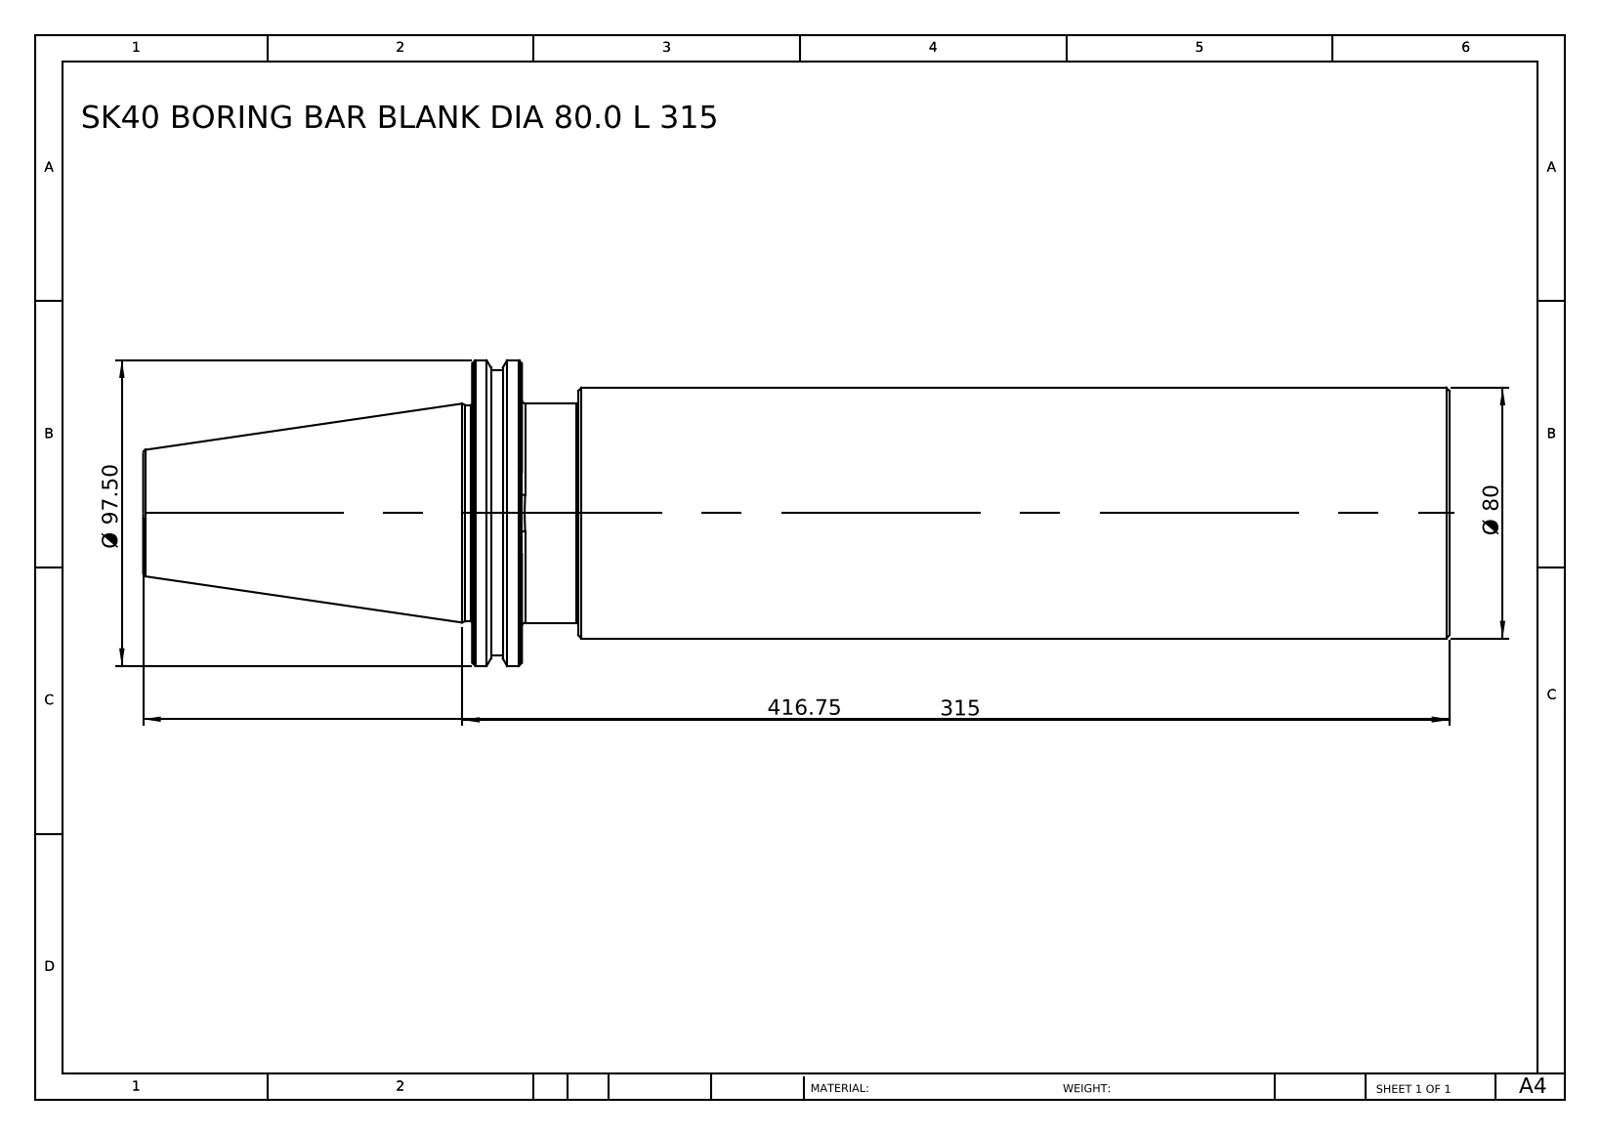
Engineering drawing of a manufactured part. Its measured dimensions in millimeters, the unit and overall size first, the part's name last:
Units: millimetres
Overall size (bounding box): 416.75 × 97.5 × 97.5
Round bosses / shafts (diameter × count): ⌀97.5 ×1, ⌀91 ×1, ⌀80 ×1, ⌀70 ×1, ⌀69 ×1
Main face-to-face distances: 311.8, 295.9, 15.9, 416.75, 120.85, 104.95, 277.9, 18, 33.9, 138.85
Volume: 1 839 000 mm³ · Surface area: 112 311 mm²
Bodies: 1 solid, 72 faces (7 planar, 12 cylindrical, 53 other)
Part name (STEP PRODUCT): SK50 BORING BAR BLANK DIA 80.0 L 315
STEP written by: SolidWorks 2014 (CONFIG_CONTROL_DESIGN)
